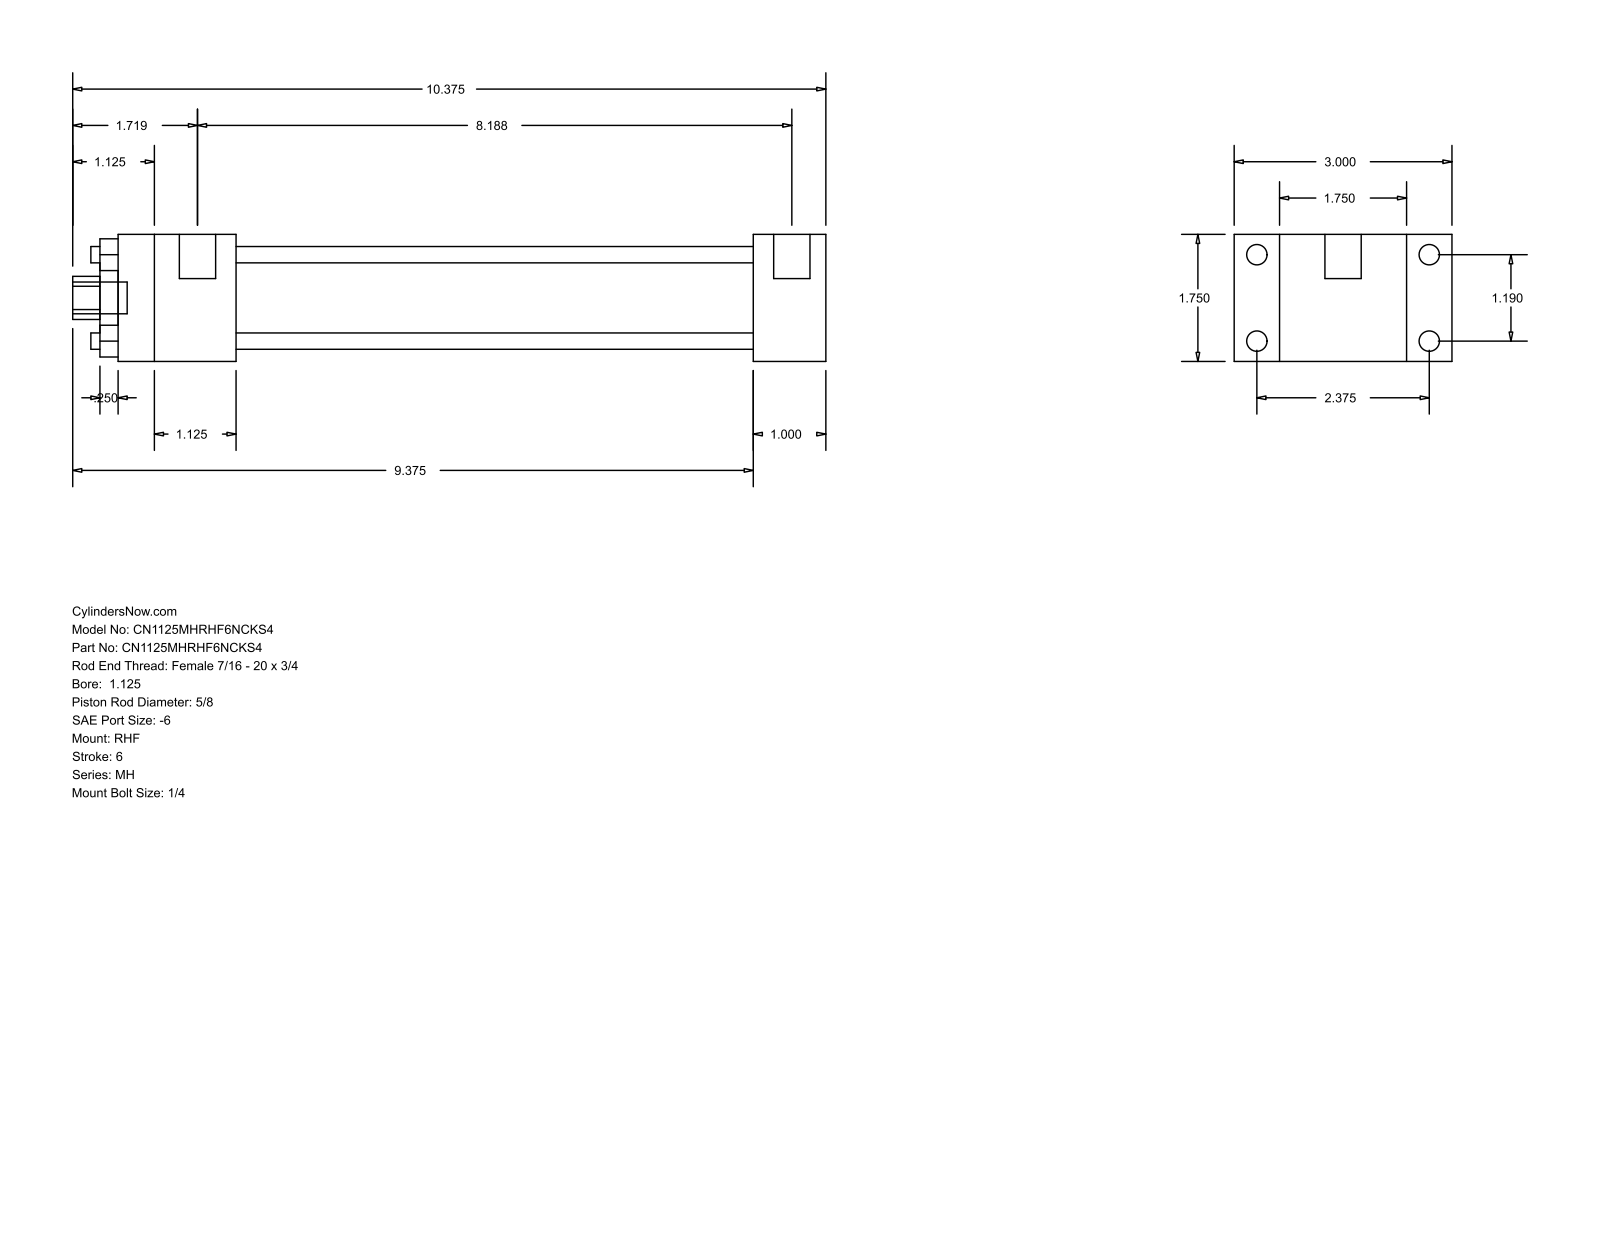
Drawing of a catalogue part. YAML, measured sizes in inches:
part_name: "MH_RHF__0112_0.625"
step_written_by: "GSSL Pune (CONFIG_CONTROL_DESIGN)"
units: inches
bodies: {solids: 0, faces: 88, planar: 60, cylindrical: 28, other: 0}
overall_size: [10.375, 3, 1.75]
round_holes:
  - {diameter: 0.225, count: 4}
  - {diameter: 0.625, count: 1}
  - {diameter: 1.125, count: 1}
  - {diameter: 1.375, count: 1}
round_bosses_or_shafts:
  - {diameter: 0.281, count: 4}
  - {diameter: 0.219, count: 4}
  - {diameter: 0.5, count: 2}
  - {diameter: 0.437, count: 1}
partial_cylinders:
  - {radius: 0.297, count: 1}
face_to_face_distances: [1.75, 0.625, 2.375, 1, 3, 7.125, 8.125, 1.625, 8.75, 9.75]
hole_center_spacings: [0.841, 1.19, 1.683]
